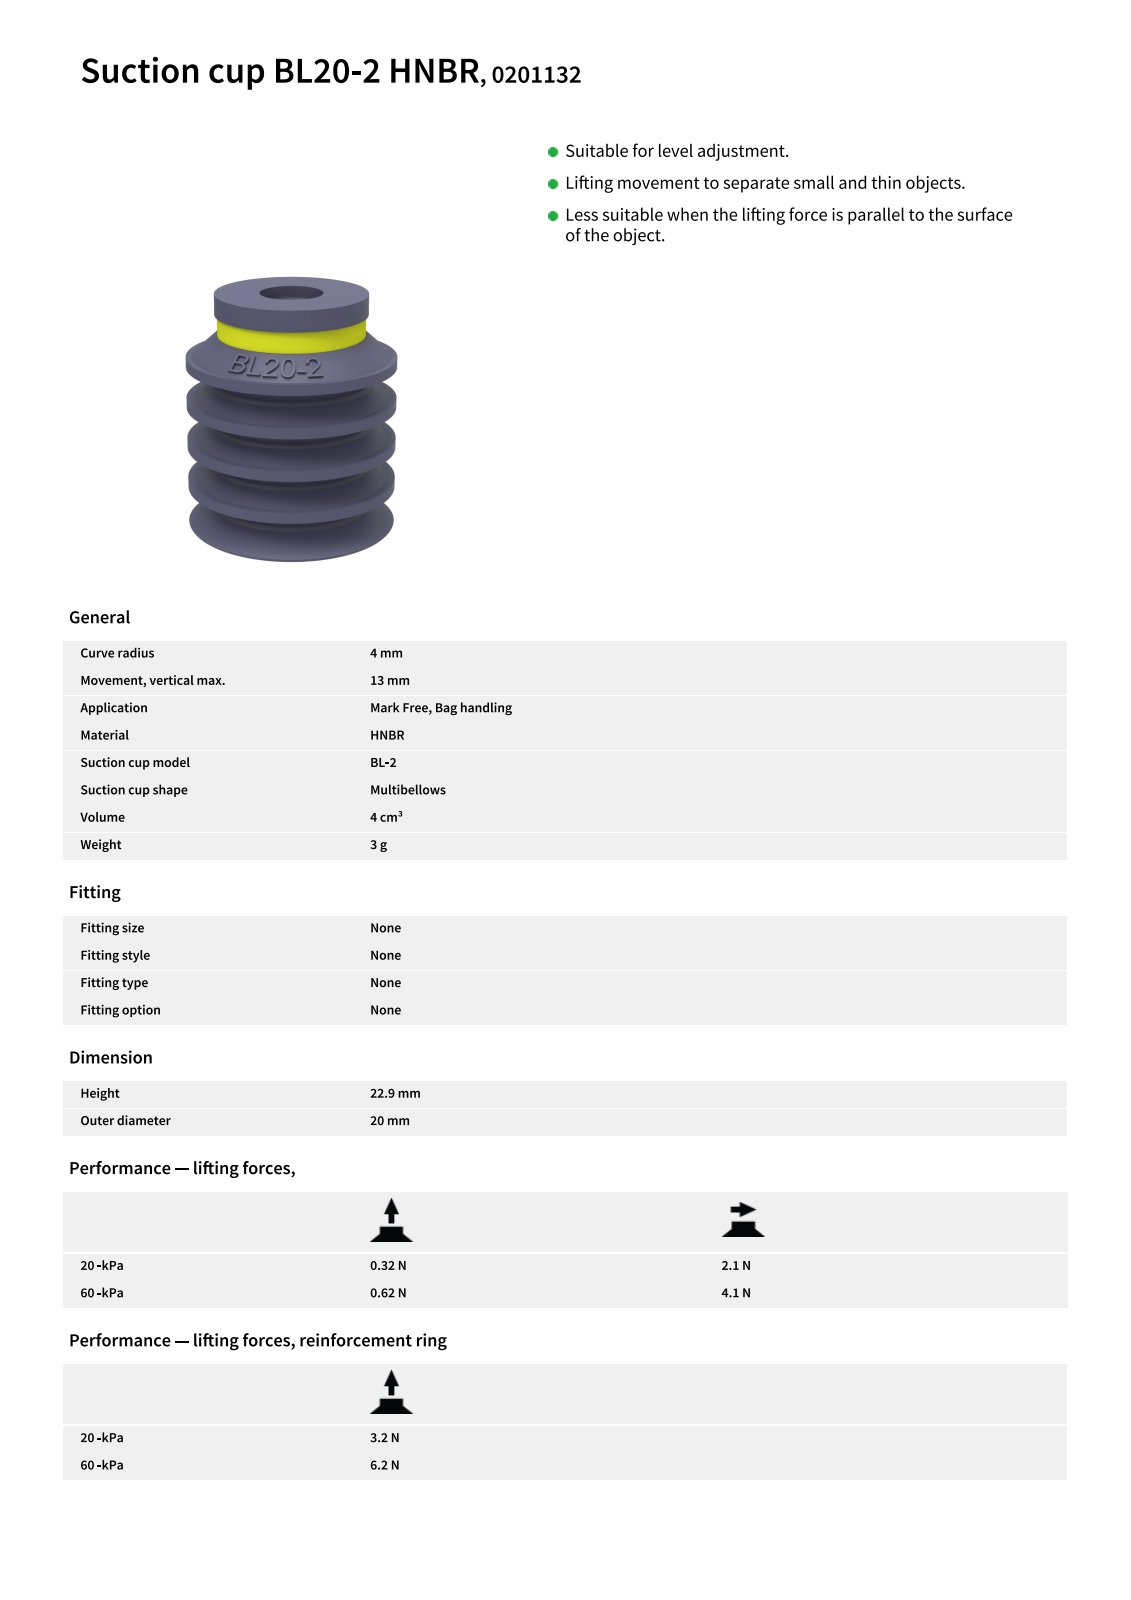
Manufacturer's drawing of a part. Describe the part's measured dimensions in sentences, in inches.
Its 3-D file was written by "Unknown (AUTOMOTIVE_DESIGN)". It is 1 solid with 256 faces: 41 planar, 25 cylindrical and 190 other. Overall it measures 0.902 by 0.787 by 0.787 inches. Its volume is 0.301 cubic inches and its surface area 4.183 square inches. Round holes: 1 of diameter 0.197, 1 of diameter 0.236. Round bosses or shafts: 1 of diameter 0.787, 1 of diameter 0.571, 1 of diameter 0.374. Partial cylindrical surfaces (rounded edges, fillets, slot ends): 2 of radius 0.004, 1 of radius 0.007, 1 of radius 0.009, 1 of radius 0.009, 1 of radius 0.009, 1 of radius 0.01, 1 of radius 0.011, 1 of radius 0.013. The main face-to-face distances are 0.157, 0.315, 0.079, 0.118, 0.276, 0.039, 0.197, 0.902, 0.433, 0.354.
